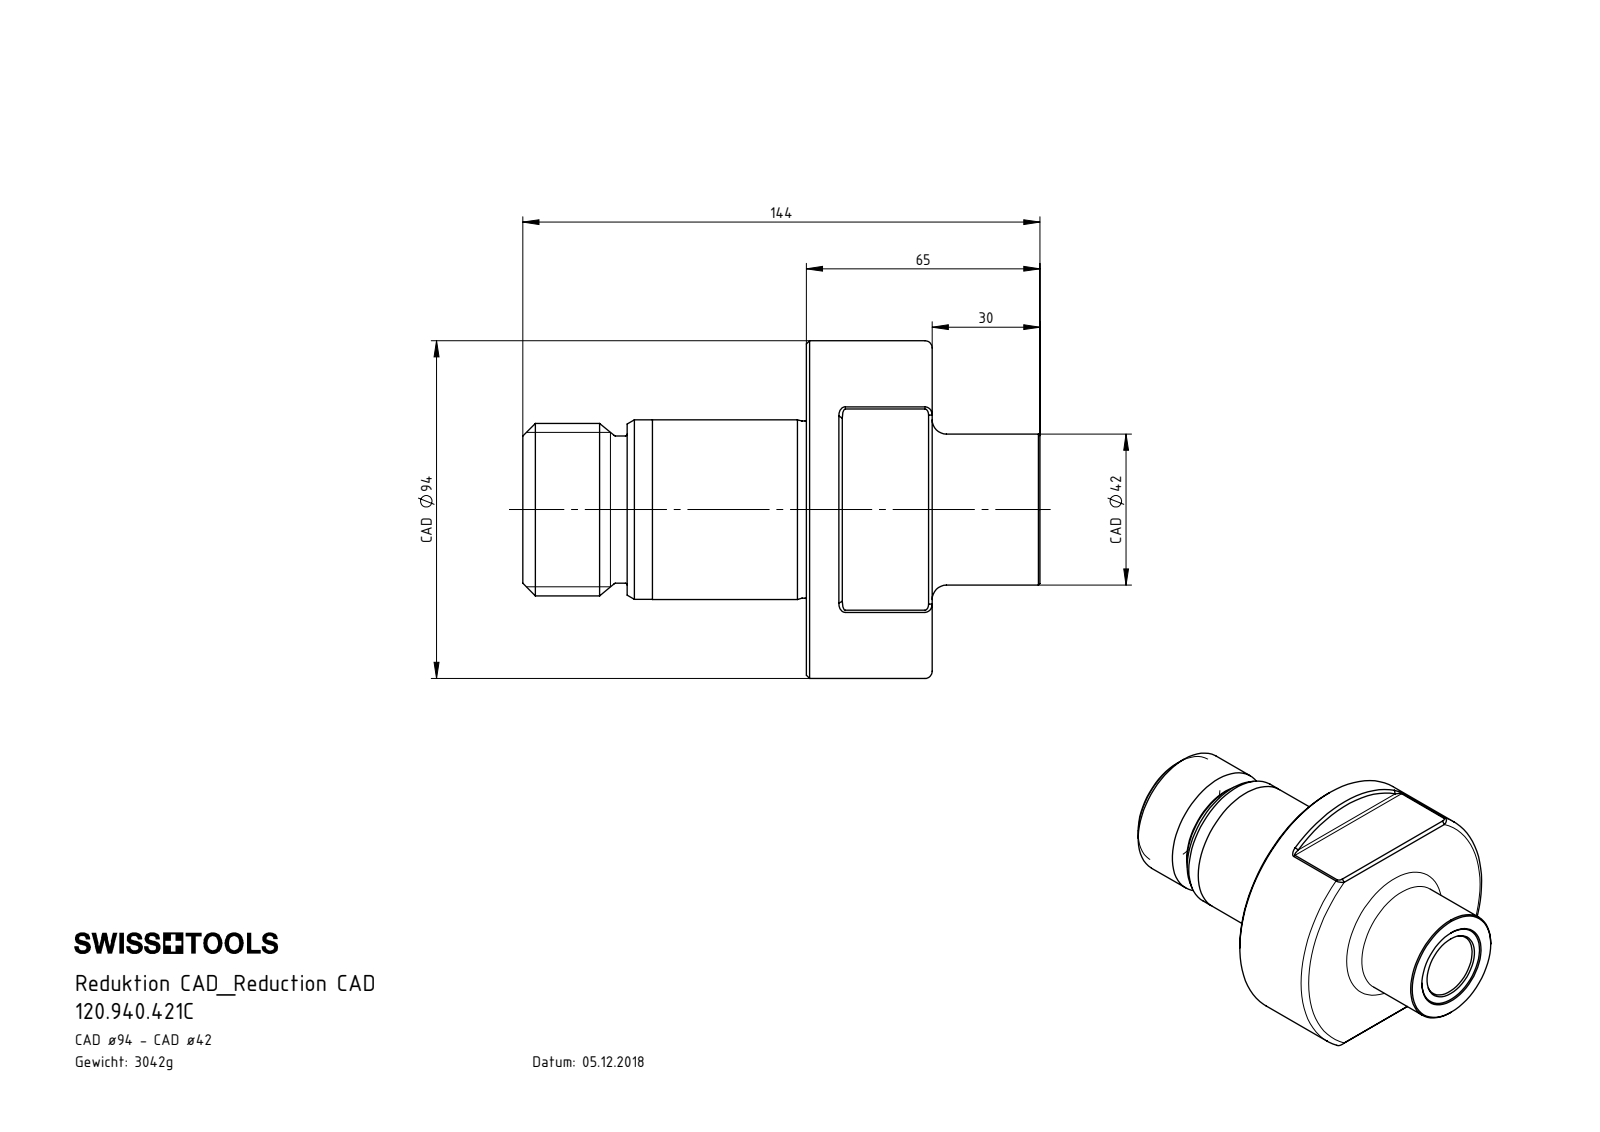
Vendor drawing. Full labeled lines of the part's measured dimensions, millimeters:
Part name (STEP PRODUCT): 120.940.421C
STEP written by: SolidWorks 2022 (CONFIG_CONTROL_DESIGN)
Units: millimetres
Bodies: 1 solid, 95 faces (18 planar, 24 cylindrical, 53 other)
Overall size (bounding box): 144 × 94 × 94
Volume: 387 534 mm³ · Surface area: 45 350 mm²
Round holes (diameter × count): ⌀8.5 ×1, ⌀19.5 ×1, ⌀24 ×1, ⌀24.7 ×1
Round bosses / shafts (diameter × count): ⌀94 ×1, ⌀50 ×1, ⌀49.95 ×1, ⌀49.3 ×1, ⌀48 ×1, ⌀42 ×1, ⌀41 ×1
Partial cylindrical surfaces — rounded edges, fillets, slot ends (radius × count): R0.8 ×2
Main face-to-face distances: 35, 75, 79, 114, 144, 65, 30, 89, 10, 25
